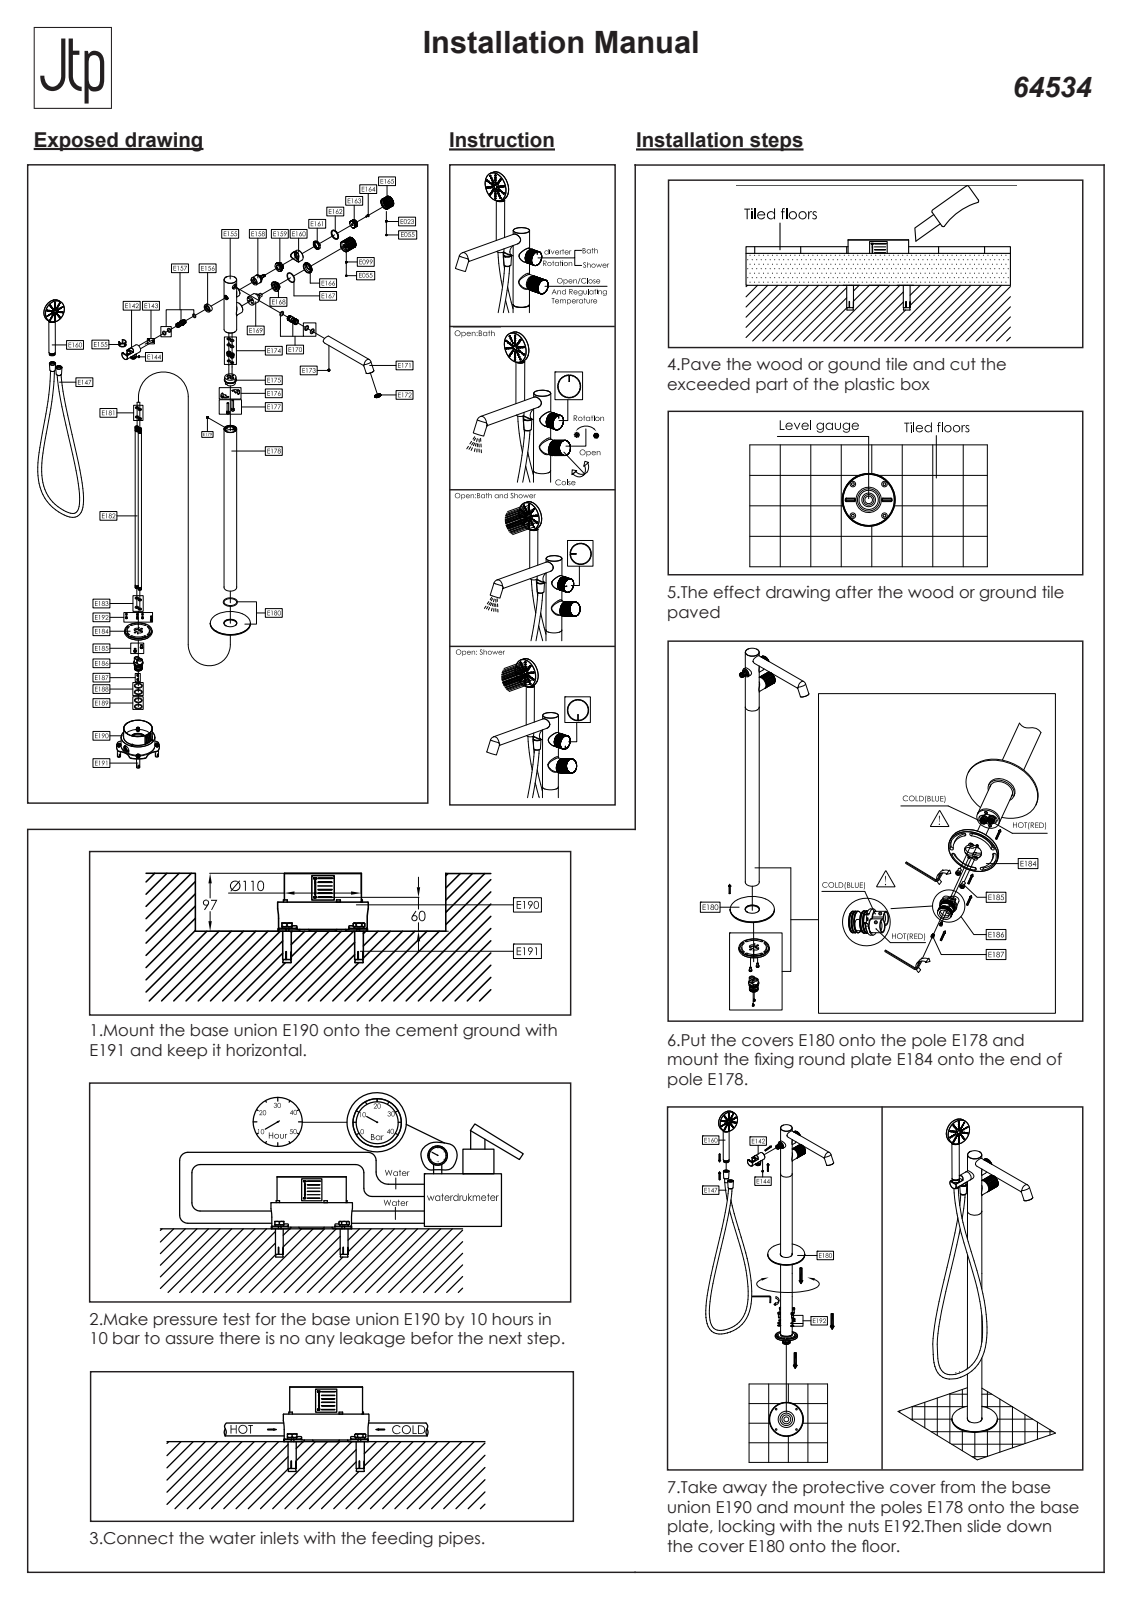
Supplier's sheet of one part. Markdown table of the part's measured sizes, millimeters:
| quantity | value |
| --- | --- |
| part name | ADMI04C89044LWPM_1; ADMI04C89044LWPM_2; 615-2512A_X2_5206_X0___X2_E1A17; M4X10_X2 (+8 more) |
| STEP written by | CREO PARAMETRIC BY PTC INC, 2019224 (CONFIG_CONTROL_DESIGN) |
| units | millimeters |
| bodies | 70 solids, 6530 faces (1612 planar, 2498 cylindrical, 2420 other) |
| overall size | 1074.03 × 345.87 × 215.85 |
| volume | 855 038 mm³ |
| surface area | 670 446 mm² |
| round holes (diameter × count) | 3.5 × 46, 1 × 45, 6 × 9, 3.3 × 8, 8 × 6, 4.5 × 5, 6.5 × 5, 7 × 5, 12 × 5, 5 × 4, 5.2 × 4, 14 × 4 |
| round bosses / shafts (diameter × count) | 3.3 × 45, 4 × 43, 10 × 8, 30 × 5, 7.5 × 5, 12.3 × 4, 5 × 4, 37 × 3 |
| partial cylindrical surfaces (radius × count) | 0.1 × 160, 0.2 × 120, 1 × 100, 0.5 × 18, 0.4 × 10, 2 × 7, 2.25 × 2, 3.79 × 2 |
| main face-to-face distances | 3, 1.5, 2.5, 8, 4, 1, 5.5, 0.8, 6.5, 11 |
| hole center spacings | 37.46, 34.81, 46.05, 7, 10.96, 21.63, 47.09, 51.13 |
